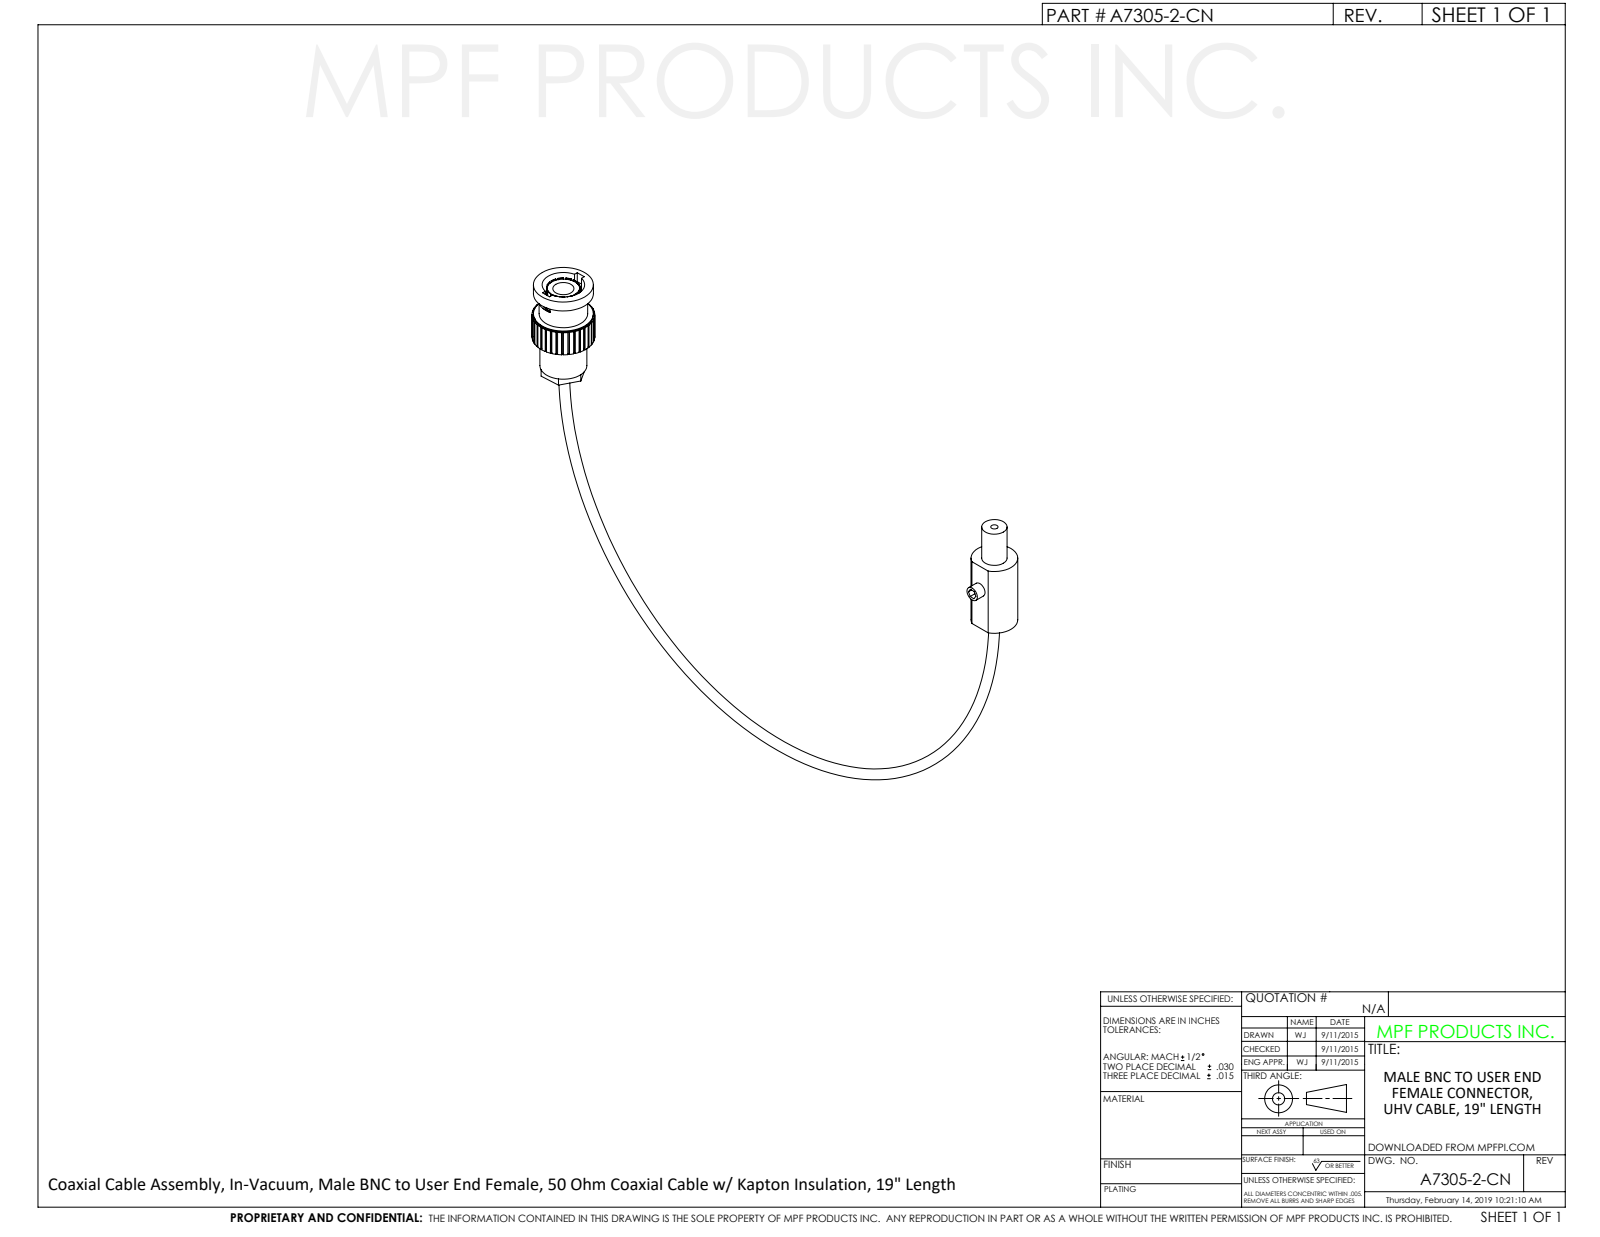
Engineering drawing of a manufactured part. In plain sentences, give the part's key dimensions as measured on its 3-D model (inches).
The part is named "A7305-2-CN". Its 3-D file was written by "SolidWorks 2012 (CONFIG_CONTROL_DESIGN)". It is 2 solids with 329 faces: 232 planar, 95 cylindrical and 2 other. Overall it measures 6.078 by 3.881 by 0.575 inches. Its volume is 0.316 cubic inches and its surface area 8.094 square inches. Round holes: 1 of diameter 0.067, 1 of diameter 0.074, 1 of diameter 0.158, 1 of diameter 0.194, 1 of diameter 0.39. Round bosses or shafts: 1 of diameter 0.55, 1 of diameter 0.525, 1 of diameter 0.445, 1 of diameter 0.43, 1 of diameter 0.428, 1 of diameter 0.308, 1 of diameter 0.233, 1 of diameter 0.134. Partial cylindrical surfaces (rounded edges, fillets, slot ends): 1 of radius 0.068, 1 of radius 0.15, 1 of radius 0.151, 1 of radius 0.287. The main face-to-face distances are 0.978, 0.693, 0.285, 0.1, 0.014, 0.54, 0.653, 0.041, 0.325, 0.878. The hole center spacings are 5.576.
